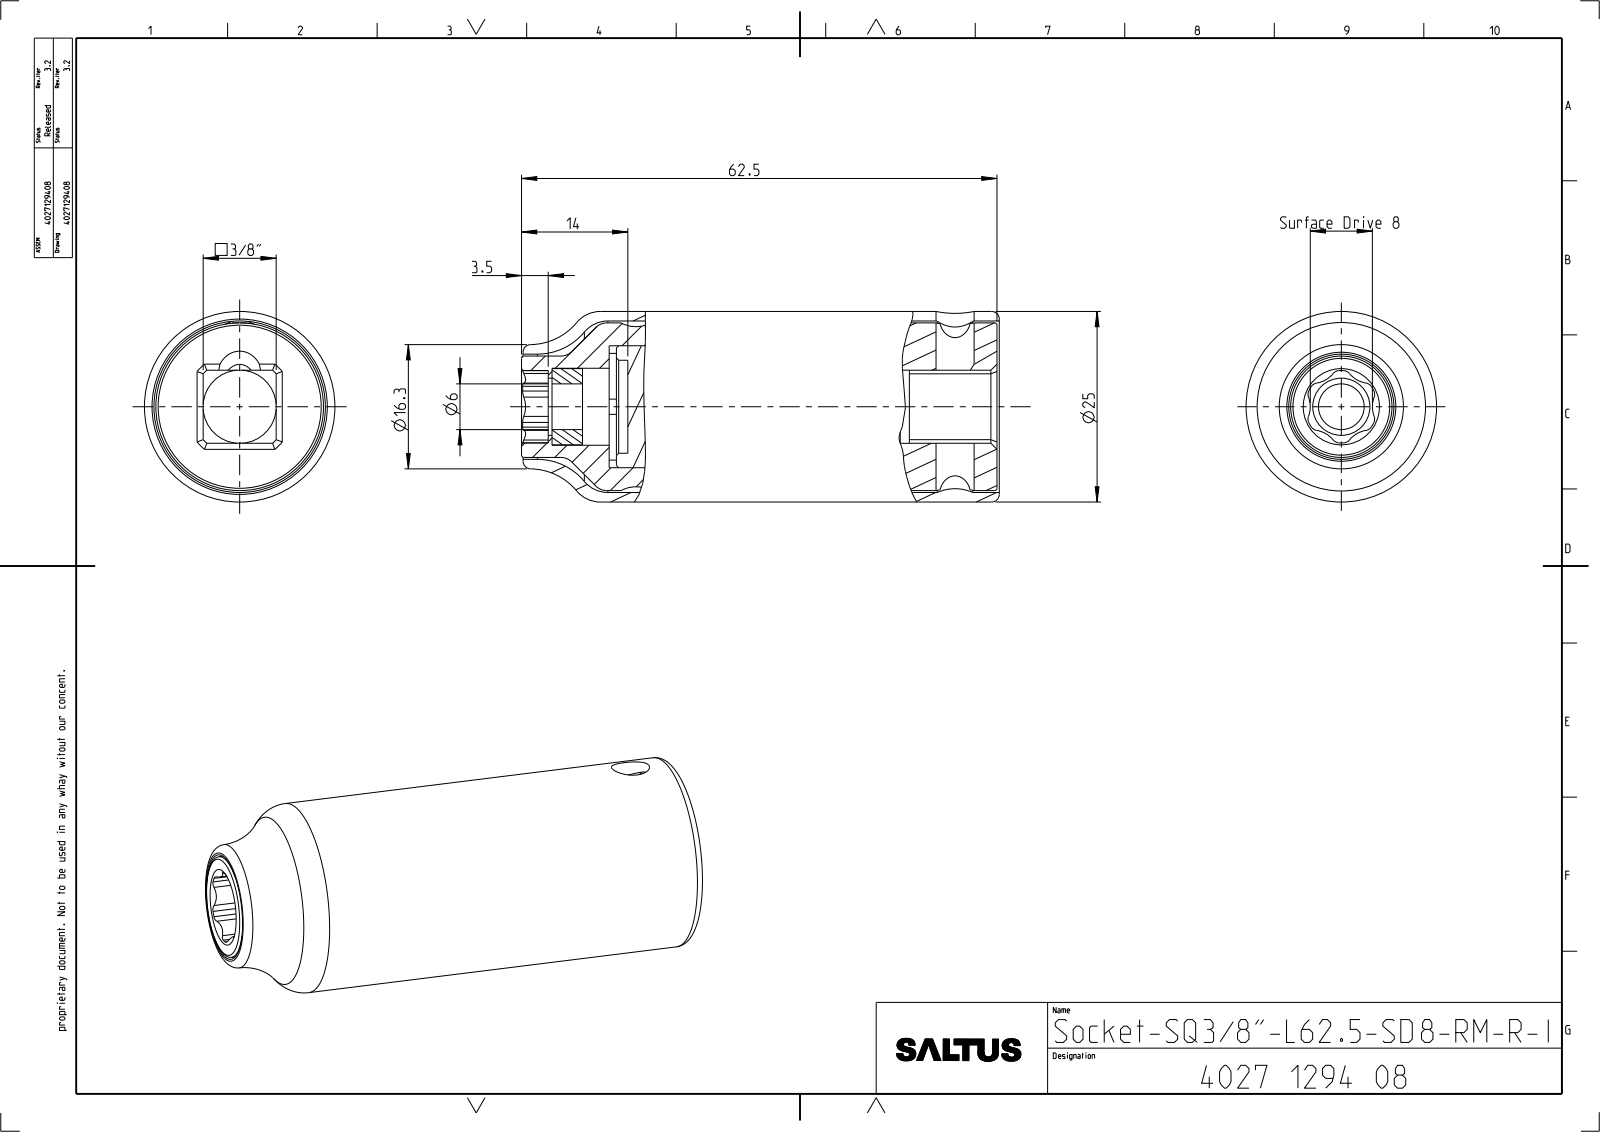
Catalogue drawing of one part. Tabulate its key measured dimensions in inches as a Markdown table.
| quantity | value |
| --- | --- |
| part name | 4027031422_AF0; 4027031423_AF0; 4027031476_AF0; 4027907728 (+4 more) |
| STEP written by | CREO PARAMETRIC BY PTC INC, 2022414 (CONFIG_CONTROL_DESIGN) |
| units | inches |
| bodies | 4 solids, 236 faces (64 planar, 120 cylindrical, 52 other) |
| overall size | 2.469 × 0.984 × 0.984 |
| volume | 0.663 in³ |
| surface area | 31.57 in² |
| round holes (diameter × count) | 0.197 × 1, 0.236 × 1, 0.295 × 1, 0.378 × 1, 0.398 × 1, 0.543 × 1, 0.886 × 1, 0.889 × 1 |
| round bosses / shafts (diameter × count) | 0.984 × 1, 0.866 × 1, 0.524 × 1, 0.394 × 1 |
| partial cylindrical surfaces (radius × count) | 0.039 × 12, 0.079 × 6, 0.138 × 6, 0.118 × 1, 0.187 × 1, 0.254 × 1 |
| main face-to-face distances | 2.004, 0.377, 0.157, 1.967, 0.037, 0.51, 1.457, 1.494, 0.5, 1.467 |
